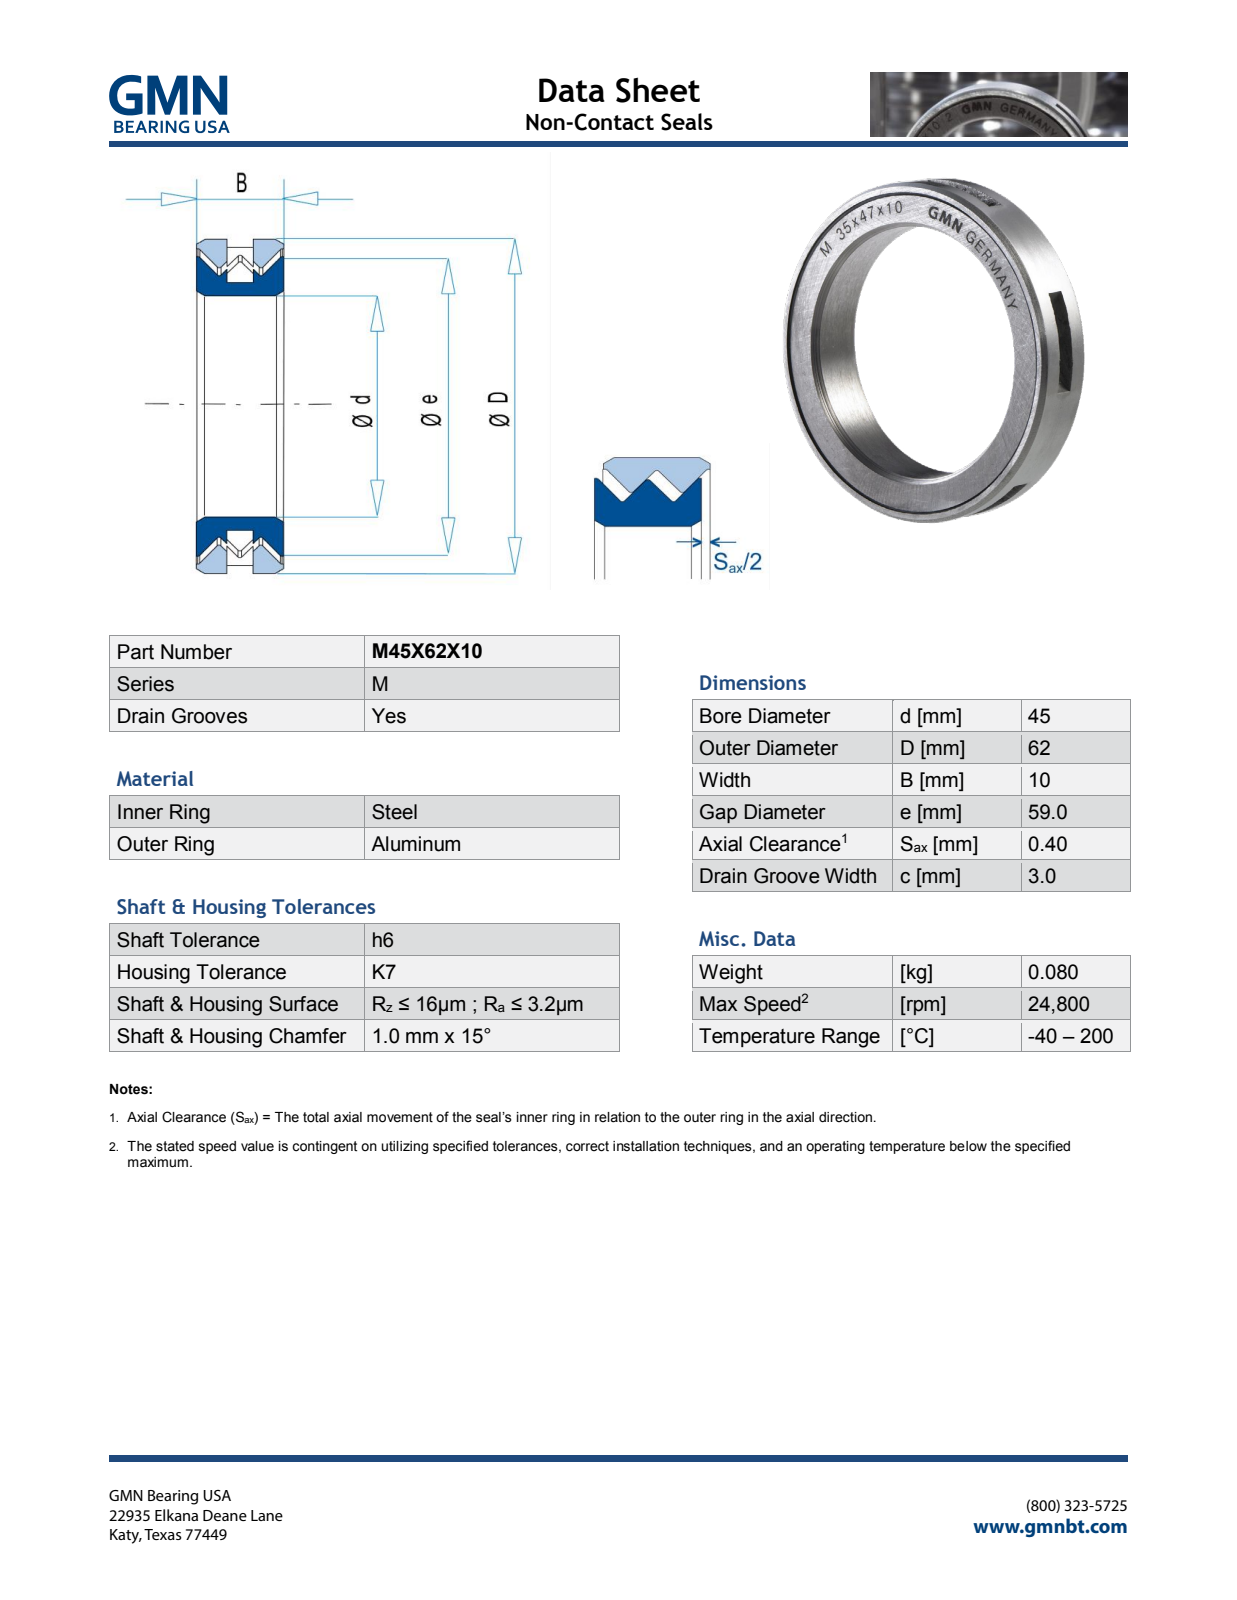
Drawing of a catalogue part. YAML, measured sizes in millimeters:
part_name: "M45X62X10_PRT"
step_written_by: "PRO/ENGINEER BY PARAMETRIC TECHNOLOGY CORPORATION, 2013150 (AUTOMOTIVE_DESIGN)"
units: millimeters
bodies: {solids: 2, faces: 617, planar: 540, cylindrical: 27, other: 50}
overall_size: [62, 62, 10.07]
volume: 12852
surface_area: 10808
round_holes:
  - {diameter: 45, count: 1}
  - {diameter: 59.28, count: 1}
round_bosses_or_shafts:
  - {diameter: 62, count: 1}
  - {diameter: 59, count: 1}
partial_cylinders:
  - {radius: 10, count: 5}
face_to_face_distances: [10, 3.5, 6.5, 3, 3.57, 6.57, 10.07, 0.55, 0.56, 4.42]
